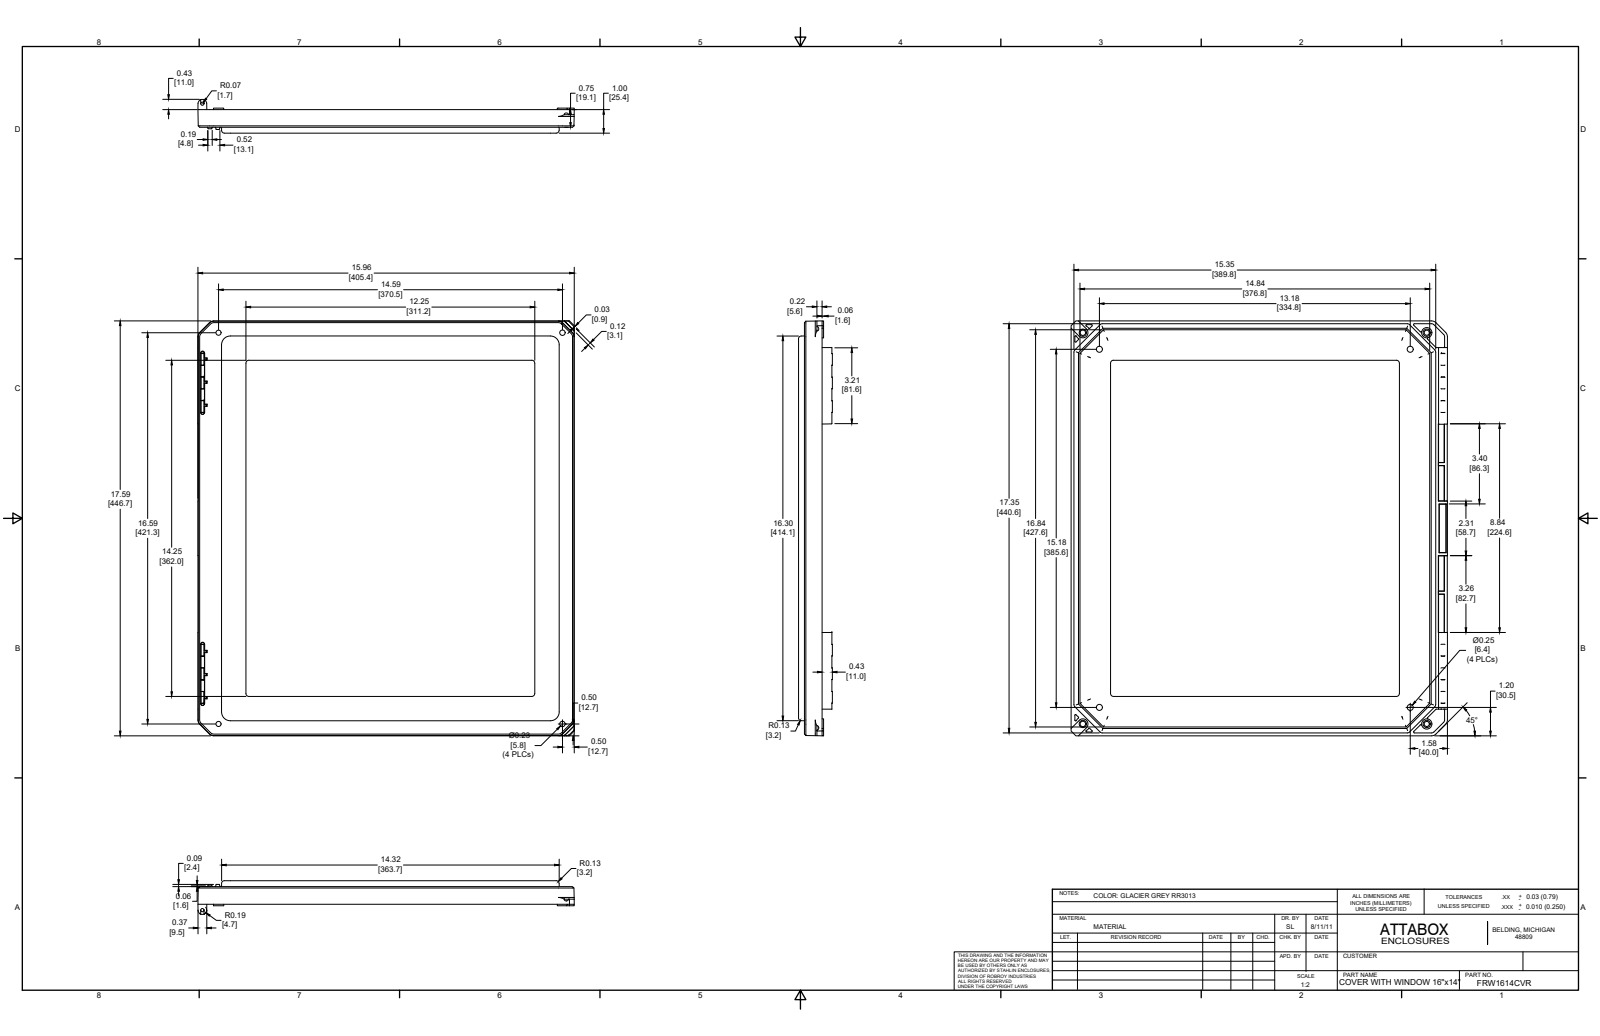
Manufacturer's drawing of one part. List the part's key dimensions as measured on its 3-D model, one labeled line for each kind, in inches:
Part name (STEP PRODUCT): FRW1614CVR
STEP written by: SolidWorks 2019 (AUTOMOTIVE_DESIGN)
Units: inches
Bodies: 1 solid, 629 faces (265 planar, 204 cylindrical, 160 other)
Overall size (bounding box): 17.585 × 15.96 × 1.434
Volume: 32.03 in³ · Surface area: 372.7 in²
Round holes (diameter × count): ⌀0.253 ×4, ⌀0.219 ×2, ⌀0.227 ×2, ⌀0.313 ×2, ⌀0.137 ×1
Round bosses / shafts (diameter × count): ⌀0.435 ×2
Partial cylindrical surfaces — rounded edges, fillets, slot ends (radius × count): R0.03 ×27, R0.01 ×18, R0.096 ×16, R0.125 ×16, R0.063 ×13, R0.062 ×11, R0.04 ×10, R0.06 ×9
Main face-to-face distances: 0.125, 0.25, 0.125, 0.375, 0.75, 0.625, 1, 0.875, 0.375, 0.625
Hole centre spacings: 15.899, 0.992, 0.993, 13.182, 13.901, 13.902, 14.585, 15.182
